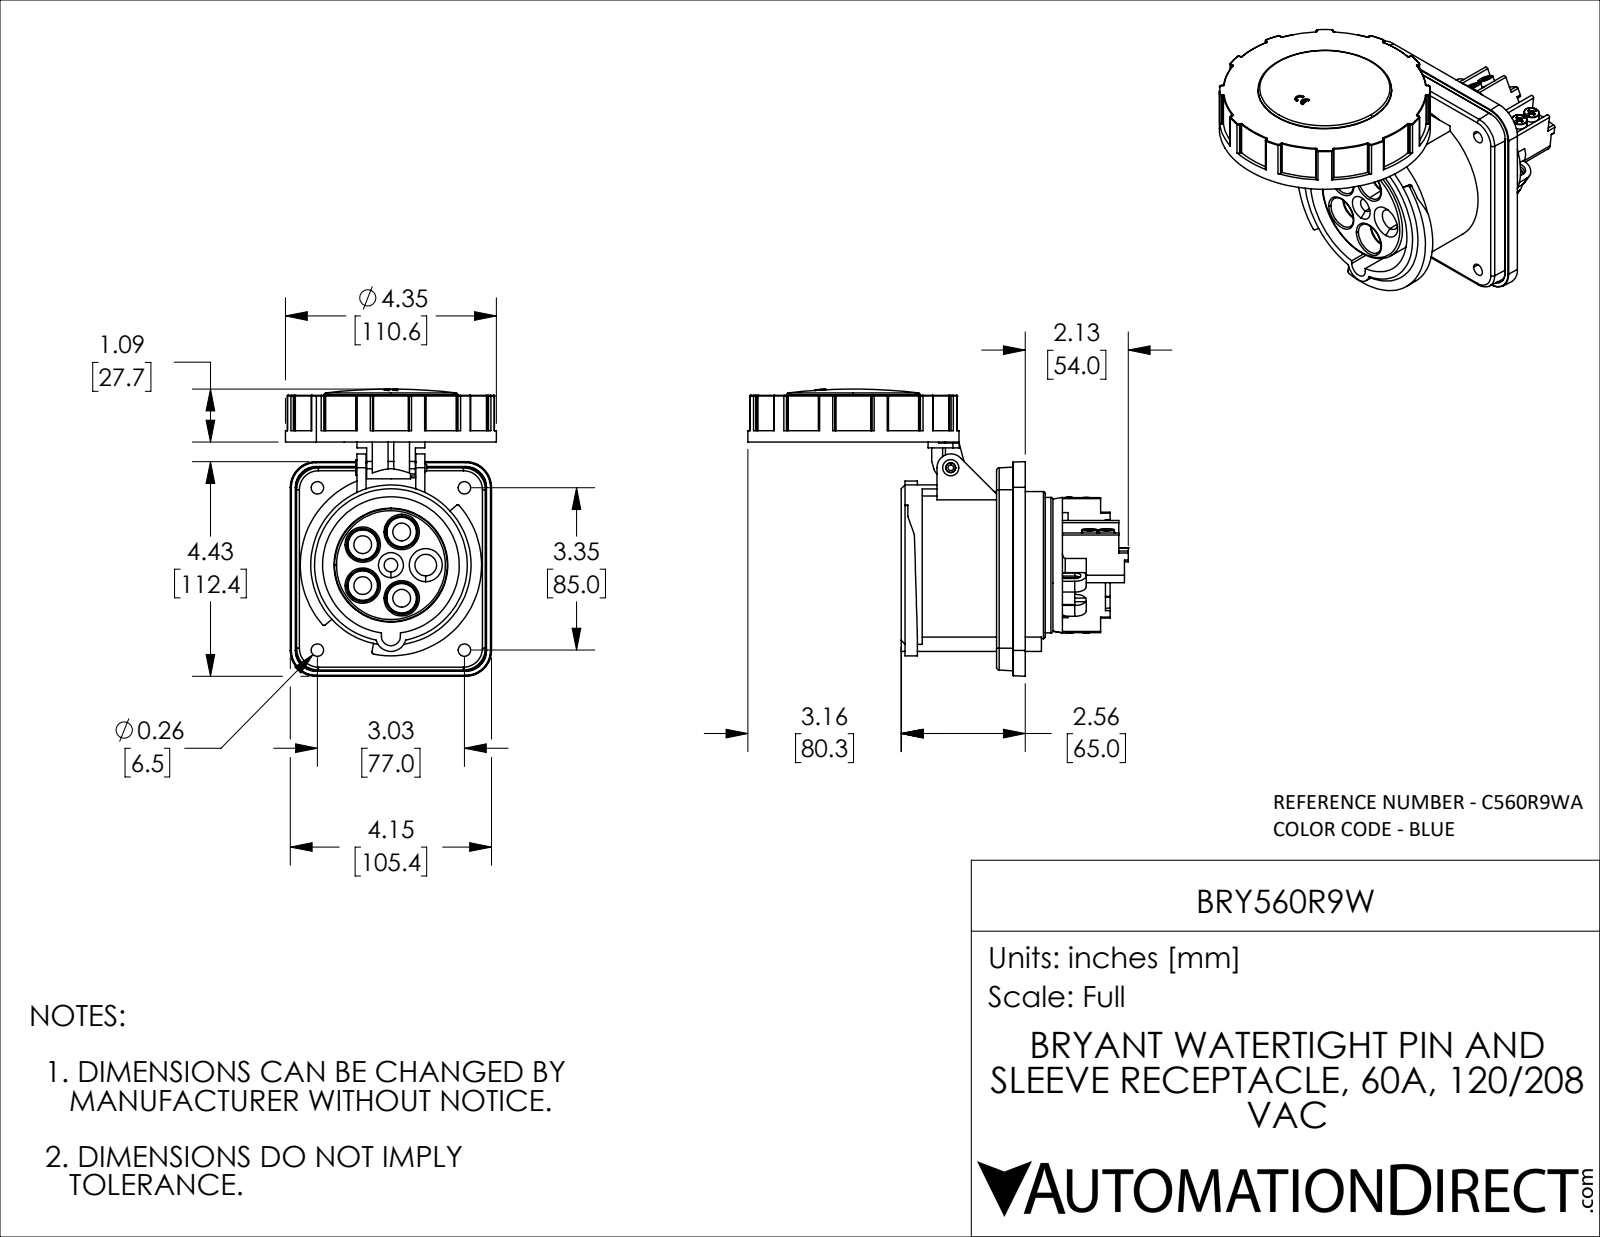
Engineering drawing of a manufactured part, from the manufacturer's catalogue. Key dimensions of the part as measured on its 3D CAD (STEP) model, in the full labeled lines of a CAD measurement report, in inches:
Part name (STEP PRODUCT): BRY560R9W
STEP written by: SolidWorks 2021 (CONFIG_CONTROL_DESIGN)
Units: inches
Bodies: 2 solids, 1788 faces (750 planar, 686 cylindrical, 352 other)
Overall size (bounding box): 7.846 × 5.919 × 4.352
Volume: 41.92 in³ · Surface area: 204.3 in²
Round holes (diameter × count): ⌀0.228 ×10, ⌀0.256 ×4, ⌀0.366 ×4, ⌀0.118 ×3, ⌀0.354 ×3, ⌀0.197 ×1, ⌀0.201 ×1, ⌀0.28 ×1, ⌀0.335 ×1, ⌀0.445 ×1, ⌀2.819 ×1, ⌀3.189 ×1
Round bosses / shafts (diameter × count): ⌀0.197 ×11, ⌀0.226 ×10, ⌀4.352 ×1, ⌀3.307 ×1, ⌀3.031 ×1, ⌀2.795 ×1, ⌀2.756 ×1, ⌀0.472 ×1
Partial cylindrical surfaces — rounded edges, fillets, slot ends (radius × count): R0.02 ×101, R0.039 ×56, R0.012 ×48, R0.01 ×28, R0.006 ×7, R0.079 ×7, R0.04 ×6, R0.05 ×6
Main face-to-face distances: 0.591, 0.846, 0.118, 2.48, 0.768, 1.89, 0.965, 0.886, 0.472, 2.362
Hole centre spacings: 0.719, 0.354, 0.845, 1.093, 1.367, 0.247, 0.558, 0.709
